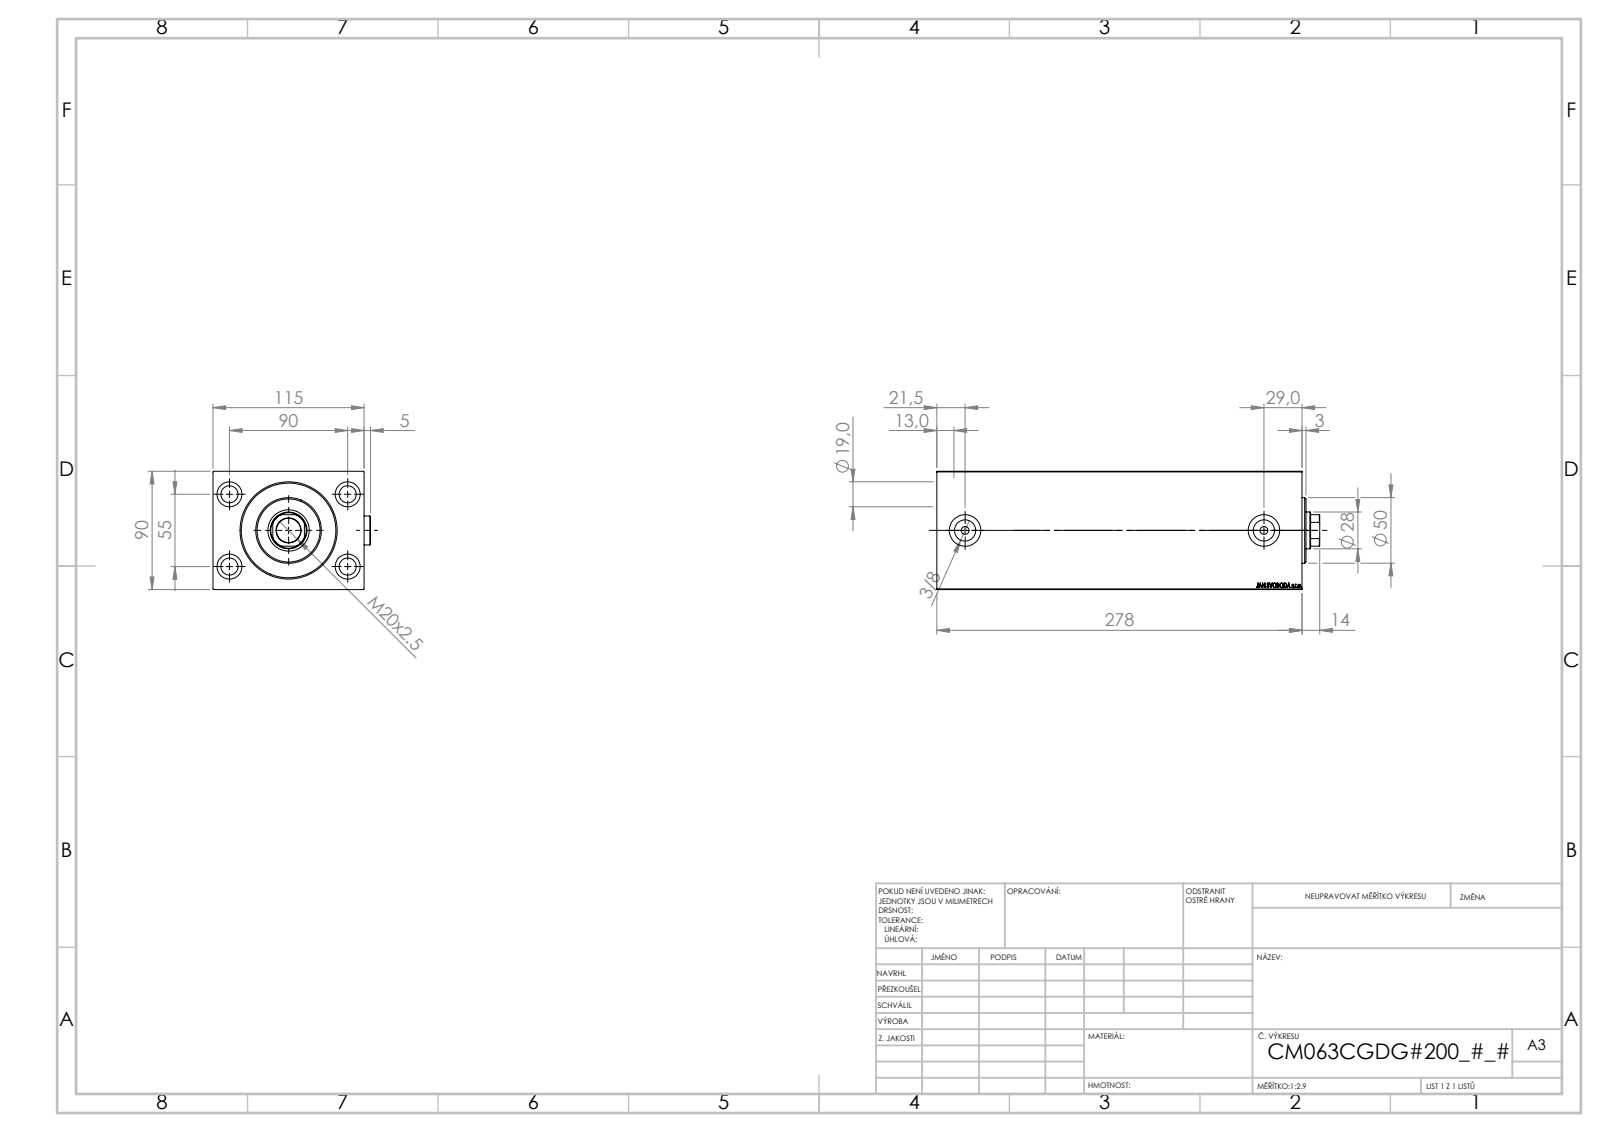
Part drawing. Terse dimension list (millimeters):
name: Zatka_OIL_PORT; V450CM_C_Body; V450CM_C_VCP; V450CM_VC_B
written by: SolidWorks 2019 (CONFIG_CONTROL_DESIGN)
unit: mm
bodies: 5 solids, 919 faces (443 planar, 78 cylindrical, 398 other)
size: 291.5 × 119.9 × 90
volume: 2 209 000 mm³; area: 286 724 mm²
holes: 4× ⌀13, 4× ⌀19, 2× ⌀6, 2× ⌀16.17, 2× ⌀24, 1× ⌀18.5, 1× ⌀28, 1× ⌀31.5, 1× ⌀63, 1× ⌀65, 1× ⌀72
bosses: 2× ⌀22, 1× ⌀50
rounds: 1× R13.5
face distances: 90, 115, 278, 17.5, 260.5, 13.5, 247, 264.5, 64.5, 213.5
hole spacings: 52.74, 55, 90, 105.48, 227.5
